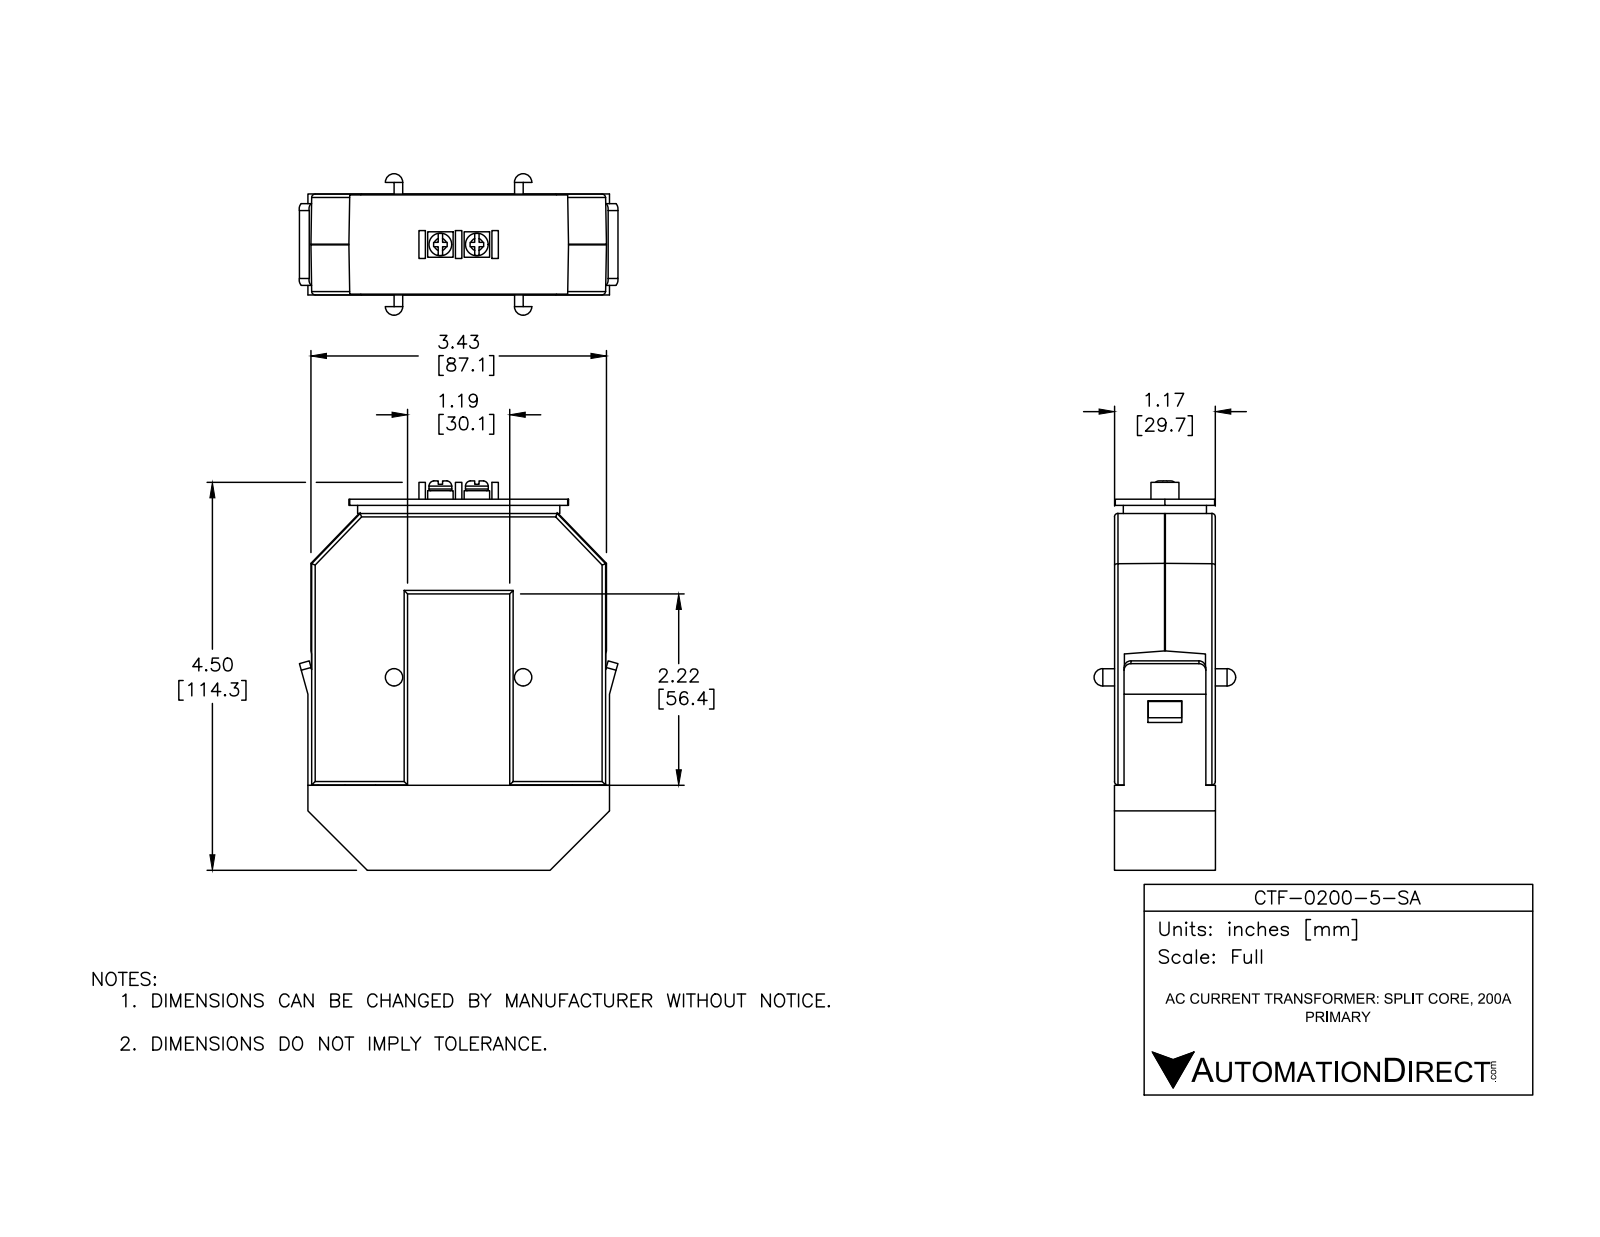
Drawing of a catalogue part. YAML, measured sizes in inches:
part_name: "CTF-0200-5-SA"
step_written_by: "SolidWorks 2016 (AUTOMOTIVE_DESIGN)"
units: inches
bodies: {solids: 8, faces: 210, planar: 160, cylindrical: 34, other: 16}
overall_size: [4.517, 3.696, 1.642]
volume: 13.27
surface_area: 62.61
round_bosses_or_shafts:
  - {diameter: 0.264, count: 2}
partial_cylinders:
  - {radius: 0.04, count: 18}
  - {radius: 0.08, count: 4}
  - {radius: 0.1, count: 2}
face_to_face_distances: [1.169, 1.17, 2.22, 3.319, 1.172, 0.118, 1.157, 2.342, 0.986, 4.305]
